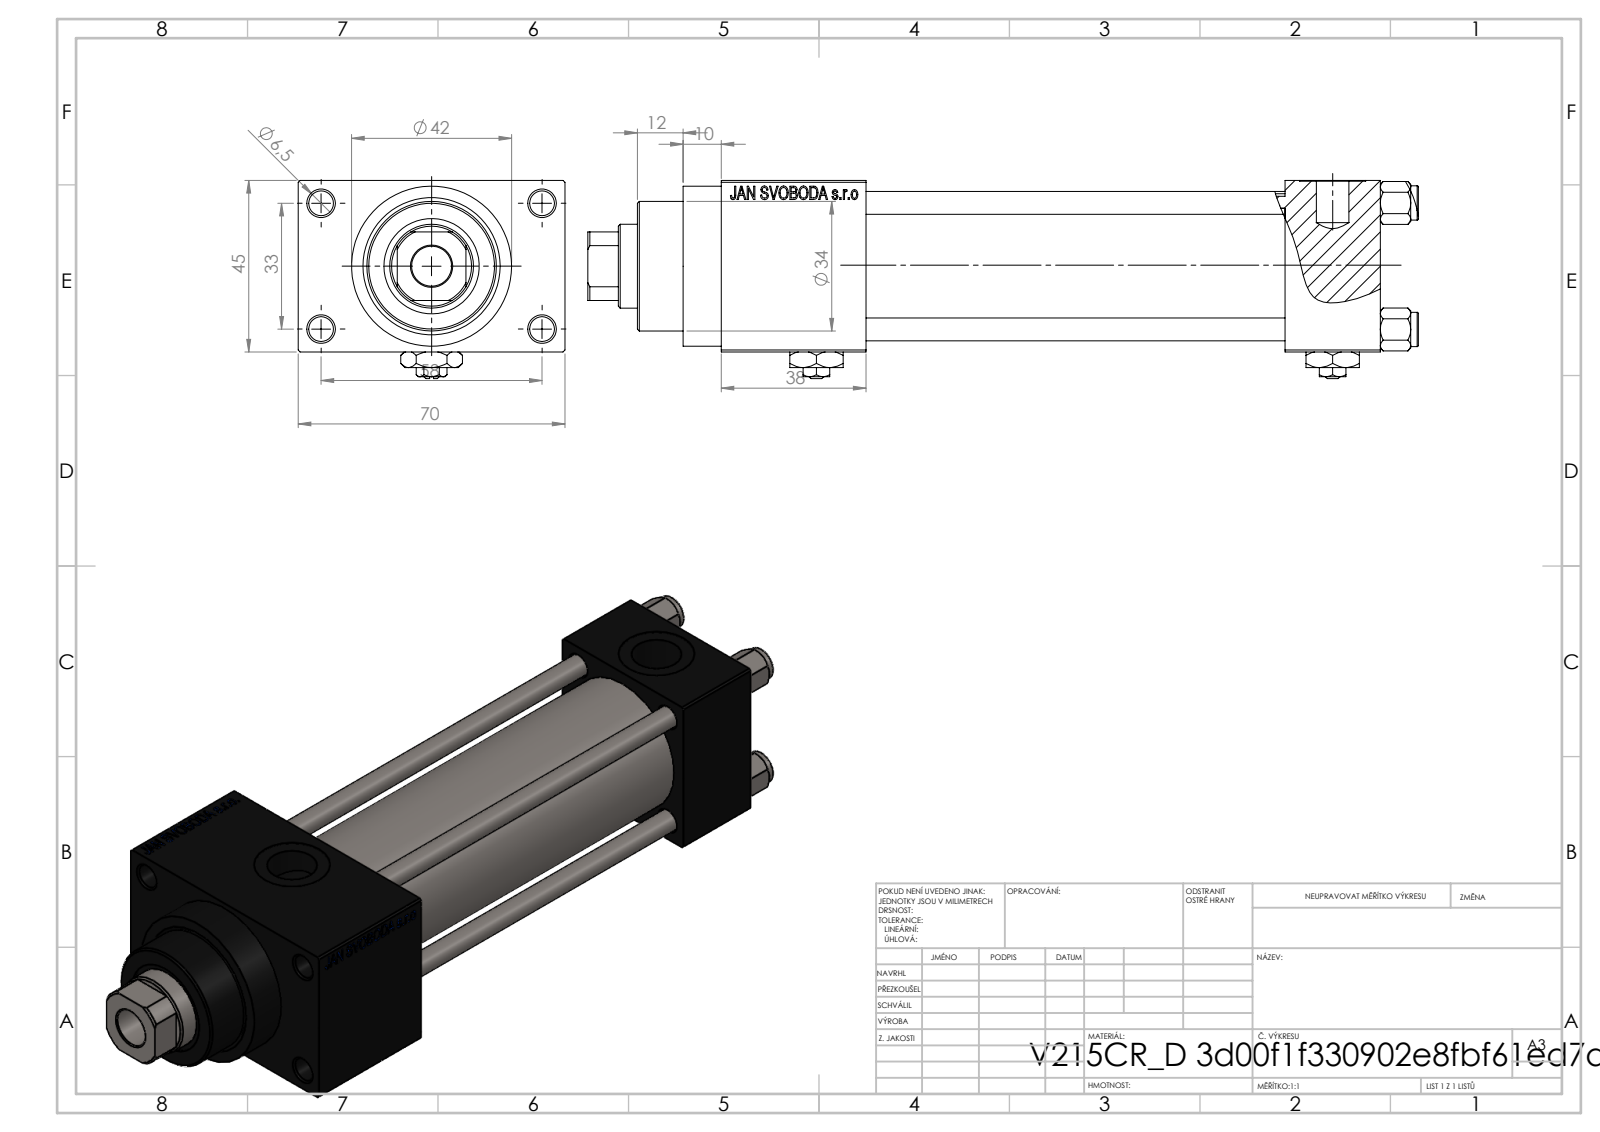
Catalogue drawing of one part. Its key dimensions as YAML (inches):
part_name: "V215_VC_A; V215CR_D_Body; V215CR_D_TYCINKA; NUT_M5_D (+2 more)"
step_written_by: "SolidWorks 2019 (CONFIG_CONTROL_DESIGN)"
units: inches
bodies: {solids: 13, faces: 1204, planar: 542, cylindrical: 100, other: 562}
overall_size: [8.583, 2.756, 2.047]
volume: 17.86
surface_area: 159.6
round_holes:
  - {diameter: 0.236, count: 4}
  - {diameter: 0.256, count: 4}
  - {diameter: 0.276, count: 2}
  - {diameter: 0.518, count: 2}
  - {diameter: 0.787, count: 2}
  - {diameter: 0.413, count: 1}
  - {diameter: 0.866, count: 1}
  - {diameter: 0.945, count: 1}
  - {diameter: 0.984, count: 1}
  - {diameter: 1.26, count: 1}
  - {diameter: 1.299, count: 1}
round_bosses_or_shafts:
  - {diameter: 0.354, count: 4}
  - {diameter: 1.654, count: 1}
  - {diameter: 1.496, count: 1}
  - {diameter: 1.339, count: 1}
partial_cylinders:
  - {radius: 0.413, count: 1}
face_to_face_distances: [1.772, 0.984, 0.492, 2.264, 4.331, 5.315, 5.827, 1.496, 2.756, 6.811]
hole_center_spacings: [0.488, 0.924, 1.307, 1.314, 1.392, 1.795, 2.219, 1.299]
